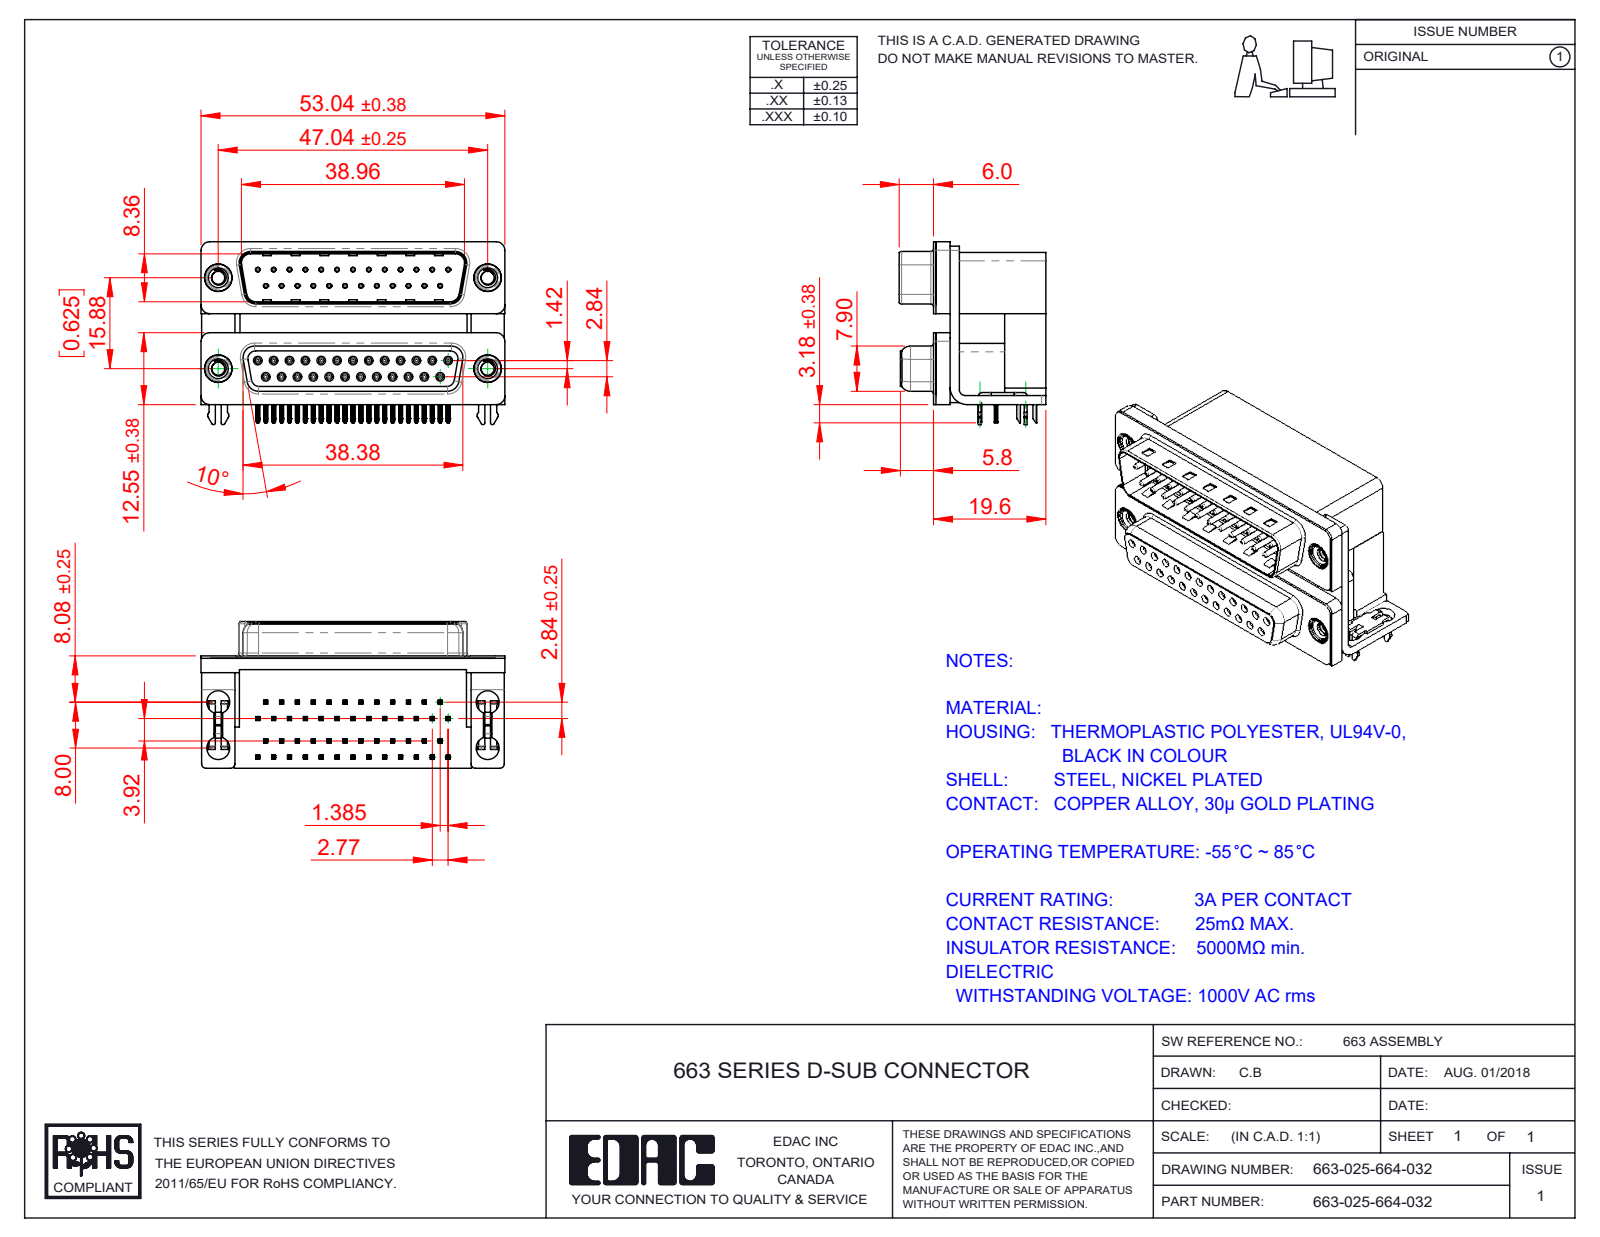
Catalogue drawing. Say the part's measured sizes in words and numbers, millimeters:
The part is named "663 Mounting Bracket_2ProngL; 663 Contact Bottom Lower; 663 Contact Top Upper_L; 663 Housing Spacer_25 Contacts L (+8 more)". Its 3-D file was written by "SolidWorks 2020 (CONFIG_CONTROL_DESIGN)". It is 63 solids with 6355 faces: 3359 planar, 1593 cylindrical and 1403 other. Overall it measures 53.04 by 31.93 by 25.6 millimeters. Its volume is 21 636 cubic millimeters and its surface area 23 275 square millimeters. Round holes: 50 of diameter 0.8, 25 of diameter 0.35, 25 of diameter 0.9, 8 of diameter 4, 4 of diameter 2.26, 4 of diameter 3.5, 4 of diameter 4.8, 4 of diameter 5. Round bosses or shafts: 25 of diameter 1.2, 25 of diameter 0.75, 4 of diameter 4.9, 4 of diameter 4.75, 4 of diameter 3.9. Partial cylindrical surfaces (rounded edges, fillets, slot ends): 202 of radius 0.1, 110 of radius 0.25, 100 of radius 0.15, 50 of radius 0.12, 50 of radius 0.35, 25 of radius 0.34, 16 of radius 0.5, 13 of radius 1.5. The main face-to-face distances are 0.4, 19.2, 7.2, 12, 10.7, 16.7, 9.5, 2.5, 15.53, 26.23. The hole center spacings are 3.16, 2.77, 5.54, 11.08, 8.31, 5.03, 13.85, 7.48.
